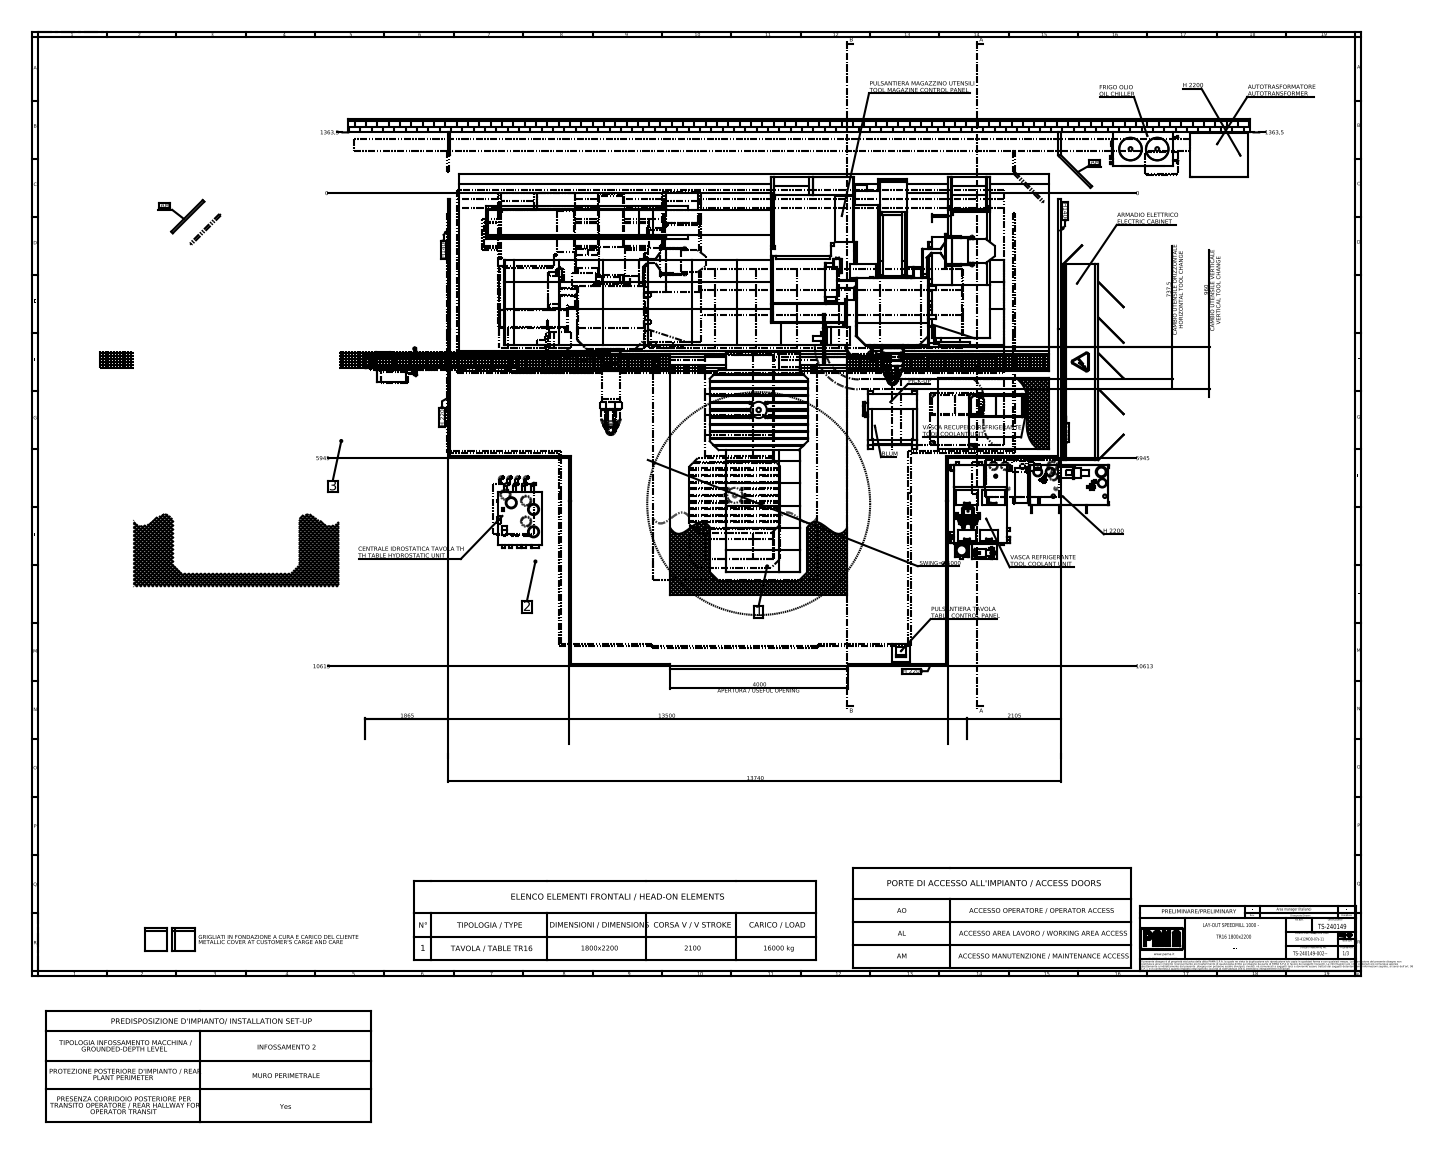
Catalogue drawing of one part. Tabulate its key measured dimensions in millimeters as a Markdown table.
| quantity | value |
| --- | --- |
| part name | S002945_default; S001790_1800x2200 (PASSO CAVA = 160) SM. 200x200; S002852_PROLUNGA (L=300); S001726_SPEEDMILL 2000-3000 (+8 more) |
| STEP written by | SolidWorks 2023 (AUTOMOTIVE_DESIGN) |
| units | millimeters |
| bodies | 450 solids, 7342 faces (5190 planar, 1566 cylindrical, 586 other) |
| overall size | 24197.11 × 15226.5 × 9400 |
| volume | 621 400 000 000 mm³ |
| surface area | 1 963 000 000 mm² |
| round holes (diameter × count) | 35 × 82, 69.6 × 63, 13 × 8, 14 × 8, 8 × 6, 32 × 6, 12.5 × 4, 50 × 3, 56.66 × 3, 4.2 × 2, 19 × 2, 30 × 2 |
| round bosses / shafts (diameter × count) | 20 × 14, 9 × 10, 30 × 8, 66.3 × 7, 60 × 7, 35 × 6, 200 × 4, 170 × 4 |
| partial cylindrical surfaces (radius × count) | 5 × 166, 15 × 46, 6 × 41, 10 × 27, 35 × 26, 3 × 20, 20 × 20, 8 × 18 |
| main face-to-face distances | 2000, 300, 50, 1340, 660, 15226.5, 14926.5, 20240, 100, 2720 |
| hole center spacings | 250, 500, 750, 1000, 1250, 1500, 1750, 2000 |
